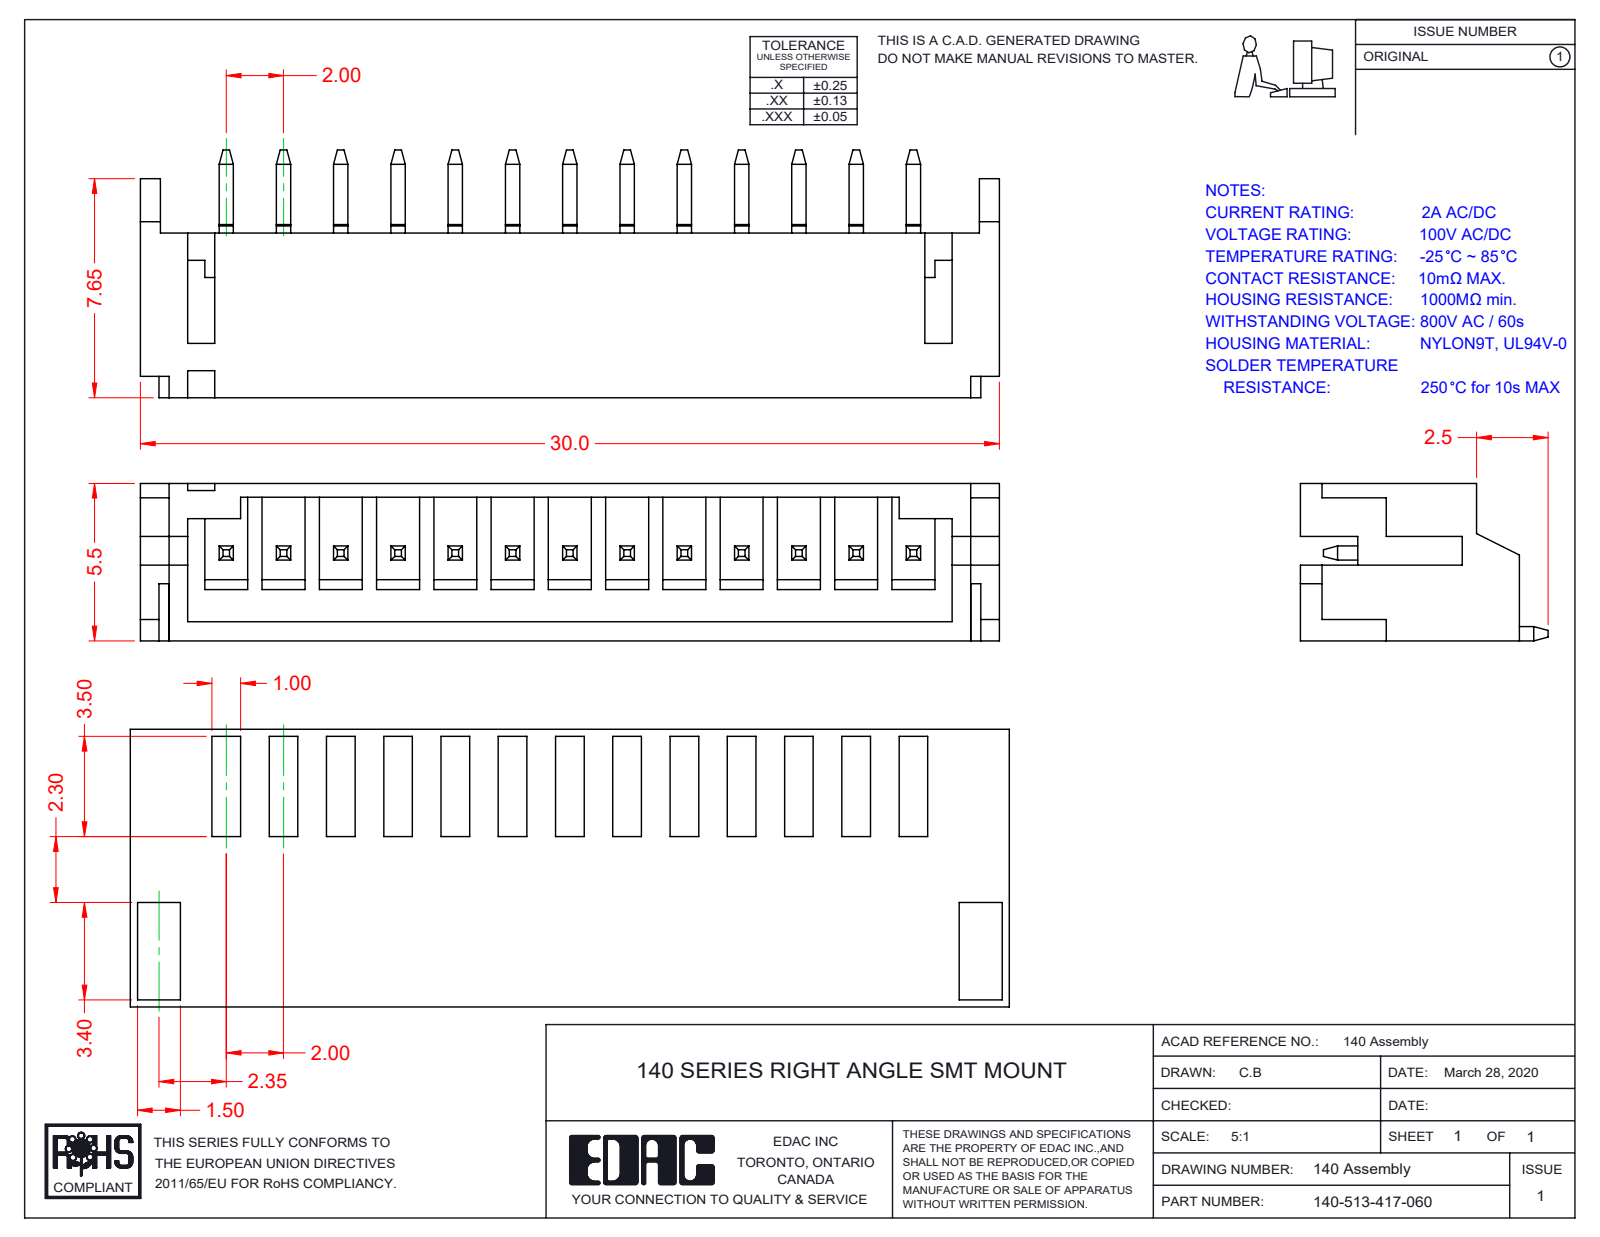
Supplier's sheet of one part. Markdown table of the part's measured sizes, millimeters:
| quantity | value |
| --- | --- |
| part name | RA SMT Contact; RA SMT Pad; 140-513-417-060; RA SMT Housing_513 |
| STEP written by | SolidWorks 2016 (CONFIG_CONTROL_DESIGN) |
| units | millimeters |
| bodies | 16 solids, 678 faces (626 planar, 52 cylindrical, 0 other) |
| overall size | 30 × 8.65 × 5.5 |
| volume | 397 mm³ |
| surface area | 1 515 mm² |
| partial cylindrical surfaces (radius × count) | 0.55 × 2 |
| main face-to-face distances | 5.5, 0.65, 0.67, 4.83, 4.35, 5.02, 0.48, 0.5, 0.95, 1 |
